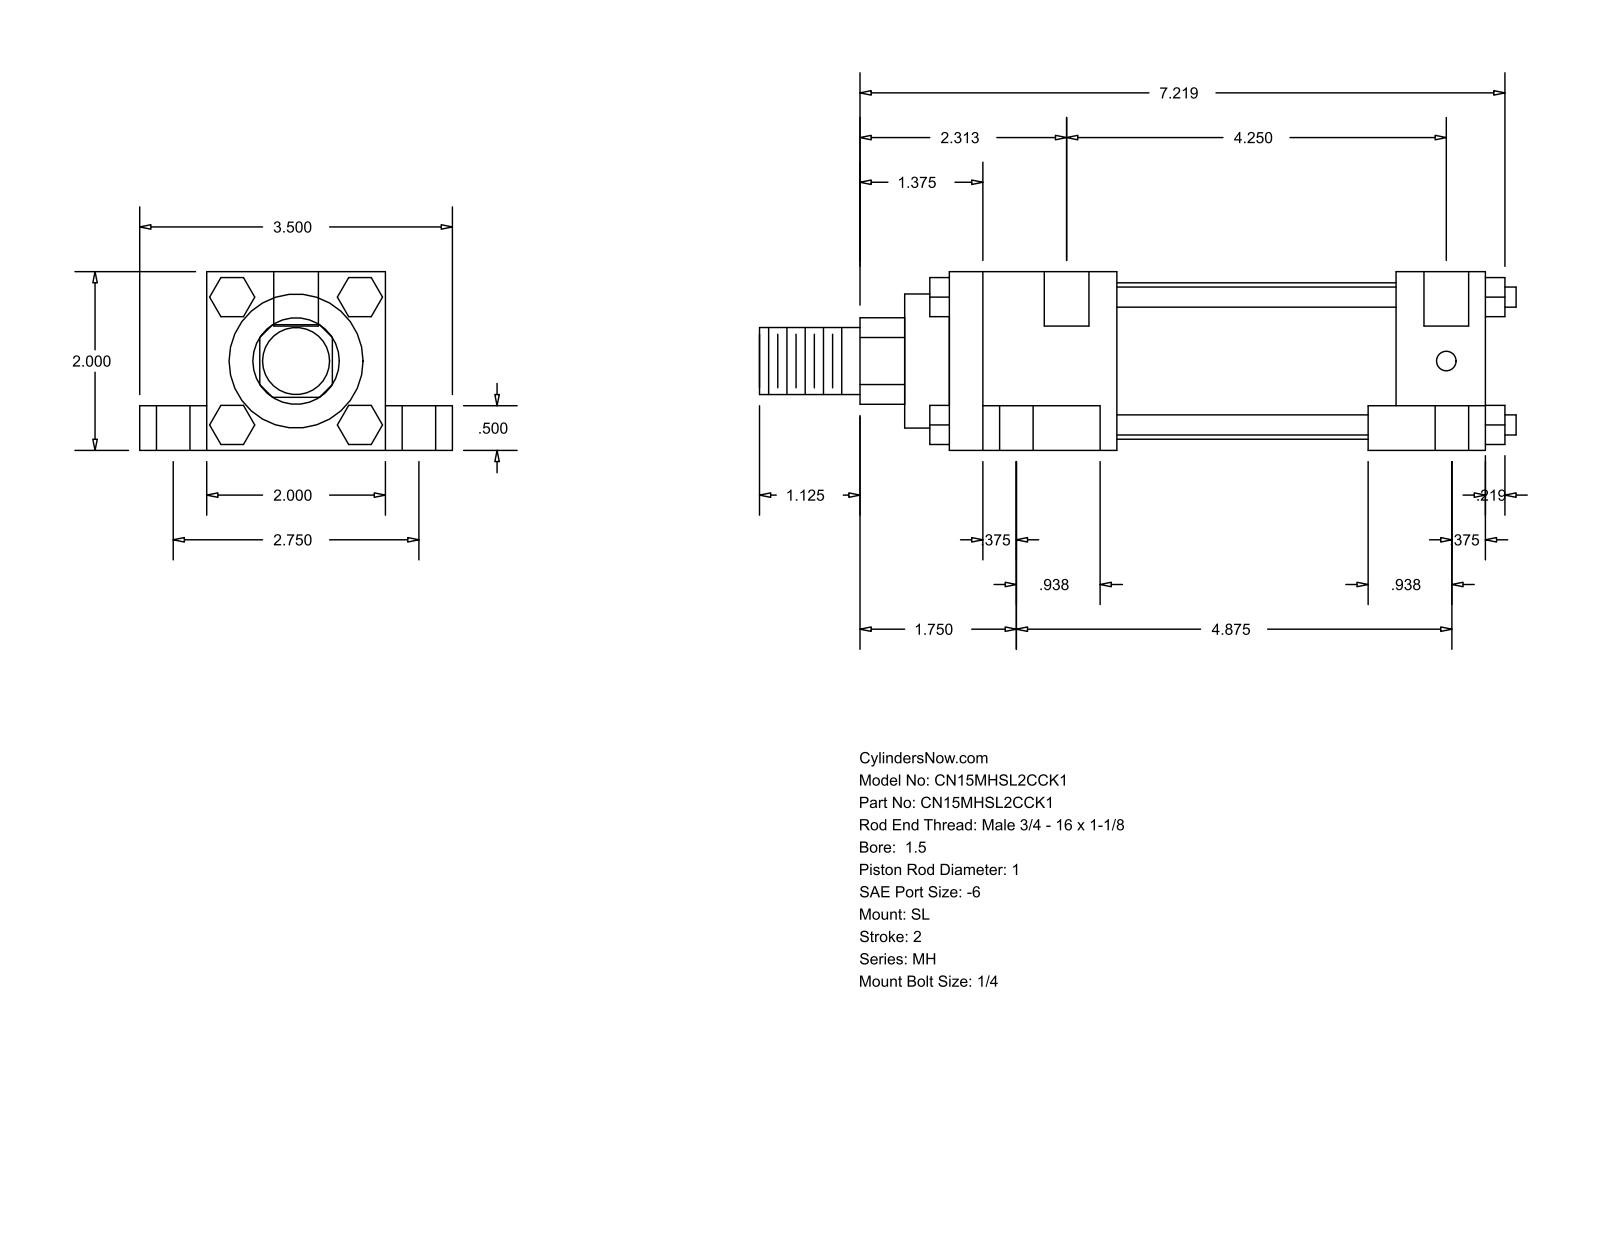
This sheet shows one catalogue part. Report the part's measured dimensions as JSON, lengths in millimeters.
{"part_name": "MH_SL__0150_1", "step_written_by": "GSSL Pune (CONFIG_CONTROL_DESIGN)", "units": "millimeters", "bodies": {"solids": 0, "faces": 148, "planar": 112, "cylindrical": 36, "other": 0}, "overall_size": [215.11, 88.9, 50.8], "round_holes": [[5.56, 4], [9.53, 4], [15.88, 4], [12.7, 2]], "round_bosses_or_shafts": [[5.71, 4], [44.45, 1], [38.1, 1], [25.4, 1], [19.05, 1]], "partial_cylinders_radius": [[12.29, 1]], "face_to_face_distances": [50.8, 12.7, 38.1, 19.05, 69.85, 152.4, 25.4, 9.52, 33.34, 109.54], "hole_center_spacings": [34.96, 36.64, 37.73, 69.84, 111.13, 114.97, 118.01, 123.83]}
